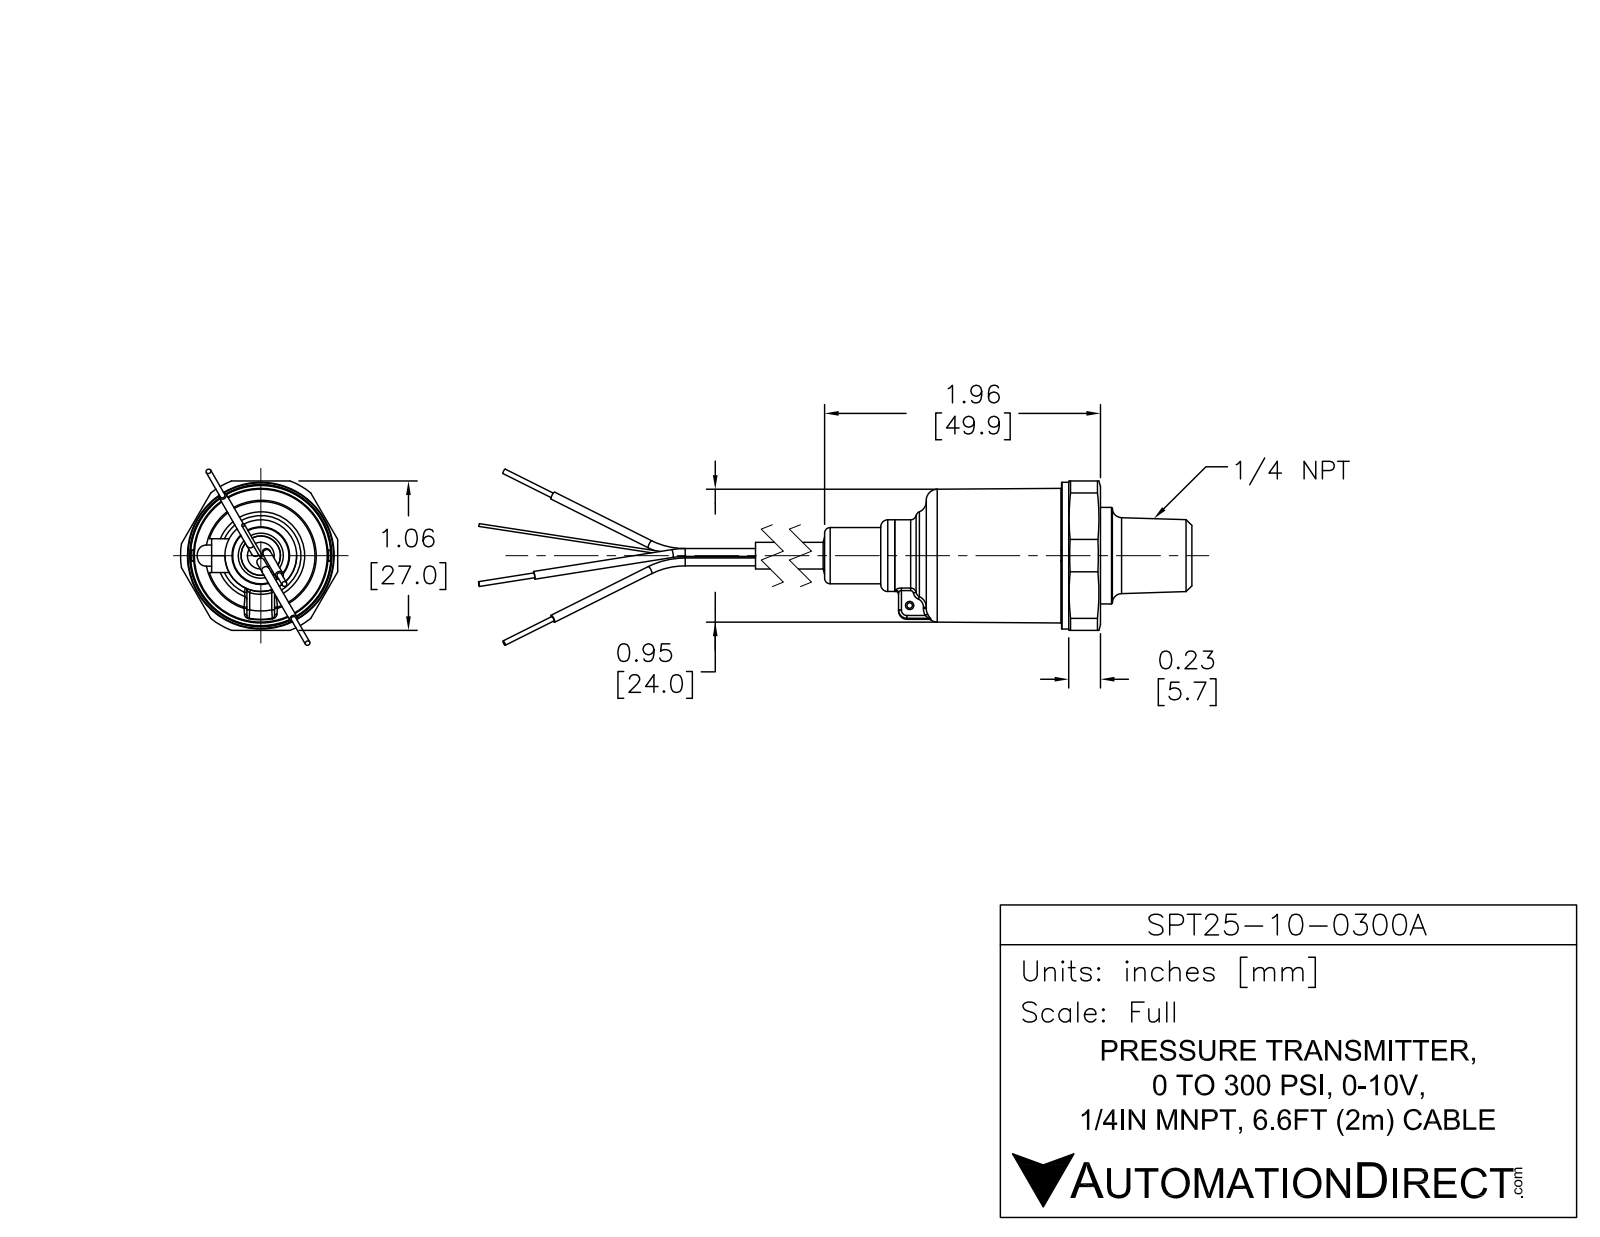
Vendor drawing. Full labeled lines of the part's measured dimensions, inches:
Part name (STEP PRODUCT): SPT25-10-0300A
STEP written by: SolidWorks 2017 (AUTOMOTIVE_DESIGN)
Units: inches
Bodies: 7 solids, 116 faces (32 planar, 49 cylindrical, 35 other)
Overall size (bounding box): 6.035 × 1.142 × 1.067
Volume: 1.269 in³ · Surface area: 11.11 in²
Round holes (diameter × count): ⌀0.039 ×1, ⌀0.13 ×1
Round bosses / shafts (diameter × count): ⌀0.055 ×6, ⌀0.03 ×5, ⌀1.053 ×1, ⌀0.945 ×1, ⌀0.689 ×1, ⌀0.551 ×1, ⌀0.512 ×1, ⌀0.394 ×1
Partial cylindrical surfaces — rounded edges, fillets, slot ends (radius × count): R0.079 ×1, R0.571 ×1
Main face-to-face distances: 0.266, 0.945, 0.679, 1.683, 1.949, 2.628, 1.732, 0.049, 0.217, 0.896
